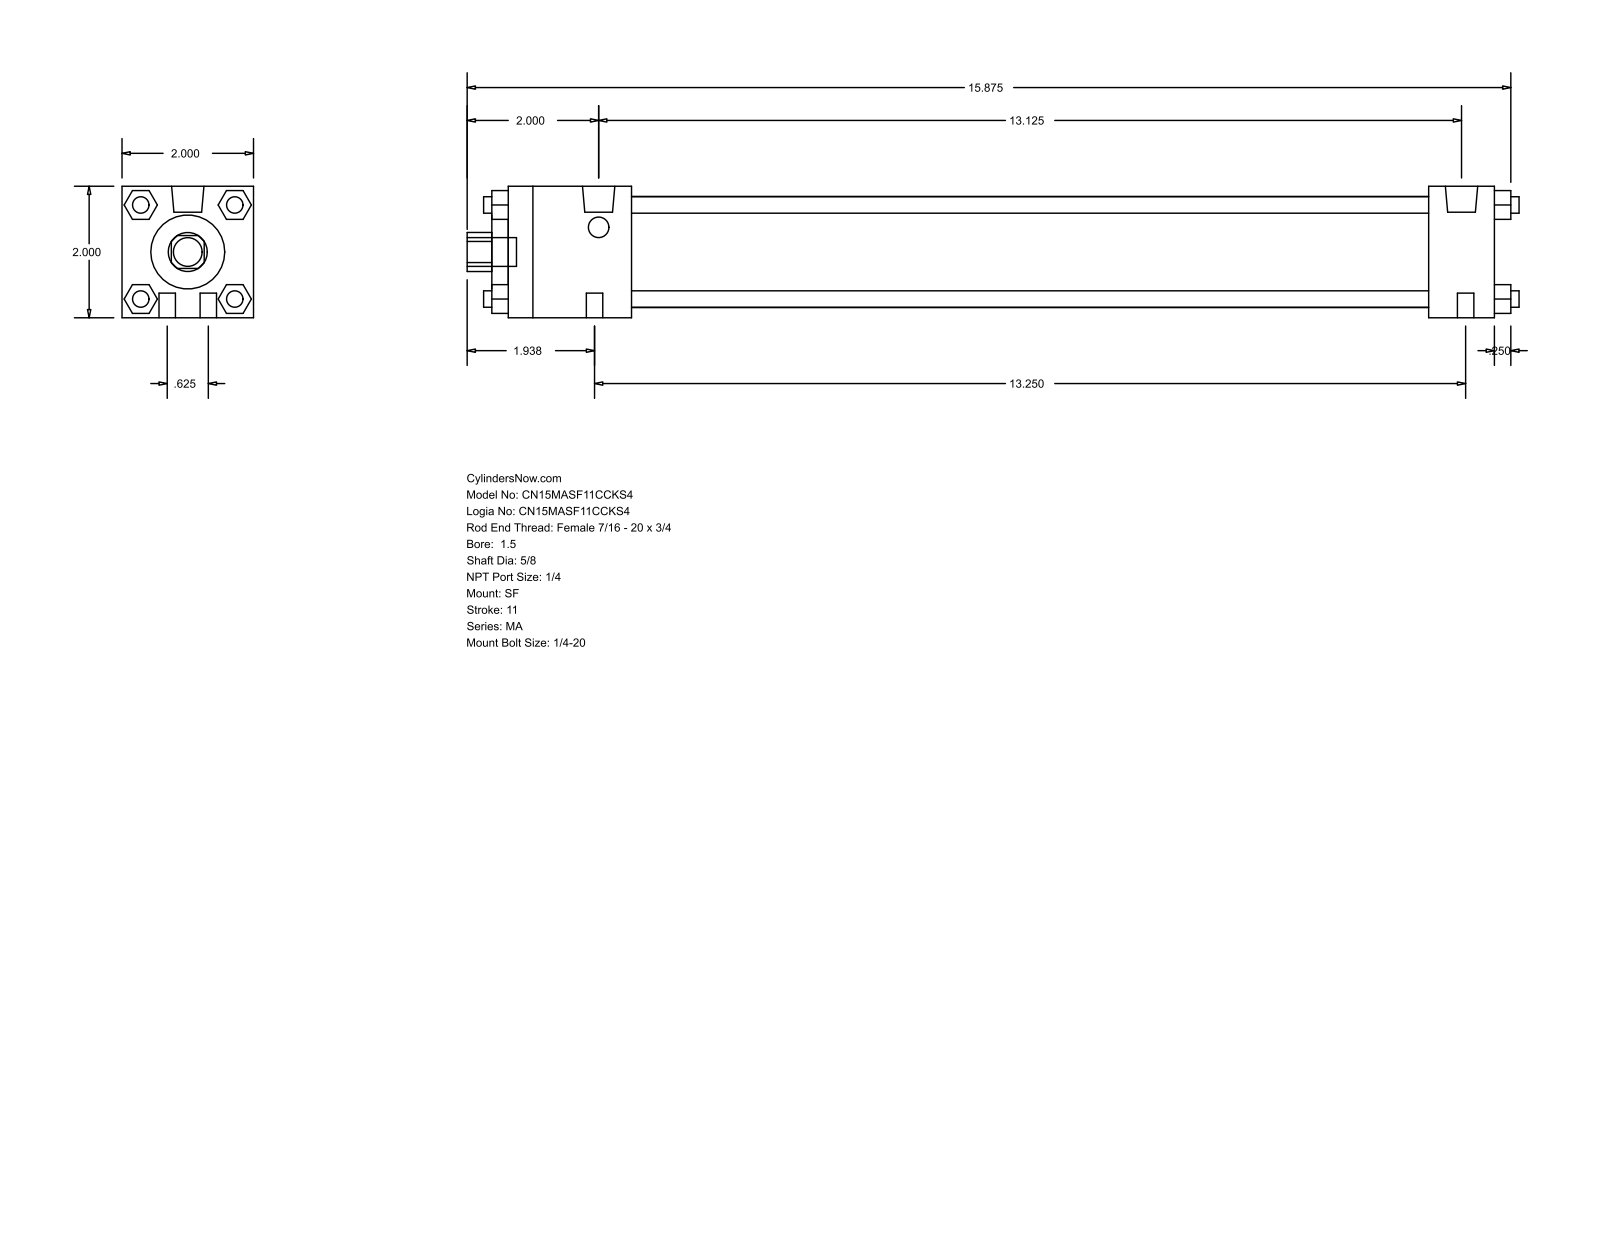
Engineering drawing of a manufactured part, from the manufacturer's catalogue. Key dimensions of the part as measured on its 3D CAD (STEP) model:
Part name (STEP PRODUCT): MA_SF__0150_0.625
STEP written by: GSSL Pune (CONFIG_CONTROL_DESIGN)
Units: millimetres
Bodies: 0 solids, 124 faces (94 planar, 30 cylindrical, 0 other)
Overall size (bounding box): 406.4 × 50.8 × 50.8
Round holes (diameter × count): ⌀15.88 ×1, ⌀28.57 ×1, ⌀42.93 ×1
Round bosses / shafts (diameter × count): ⌀6.35 ×8, ⌀12.49 ×2, ⌀7.94 ×2, ⌀11.11 ×1
Partial cylindrical surfaces — rounded edges, fillets, slot ends (radius × count): R7.54 ×1
Main face-to-face distances: 50.8, 381, 6.35, 387.35, 47.62, 355.6, 307.98, 333.38, 25.4, 53.97
